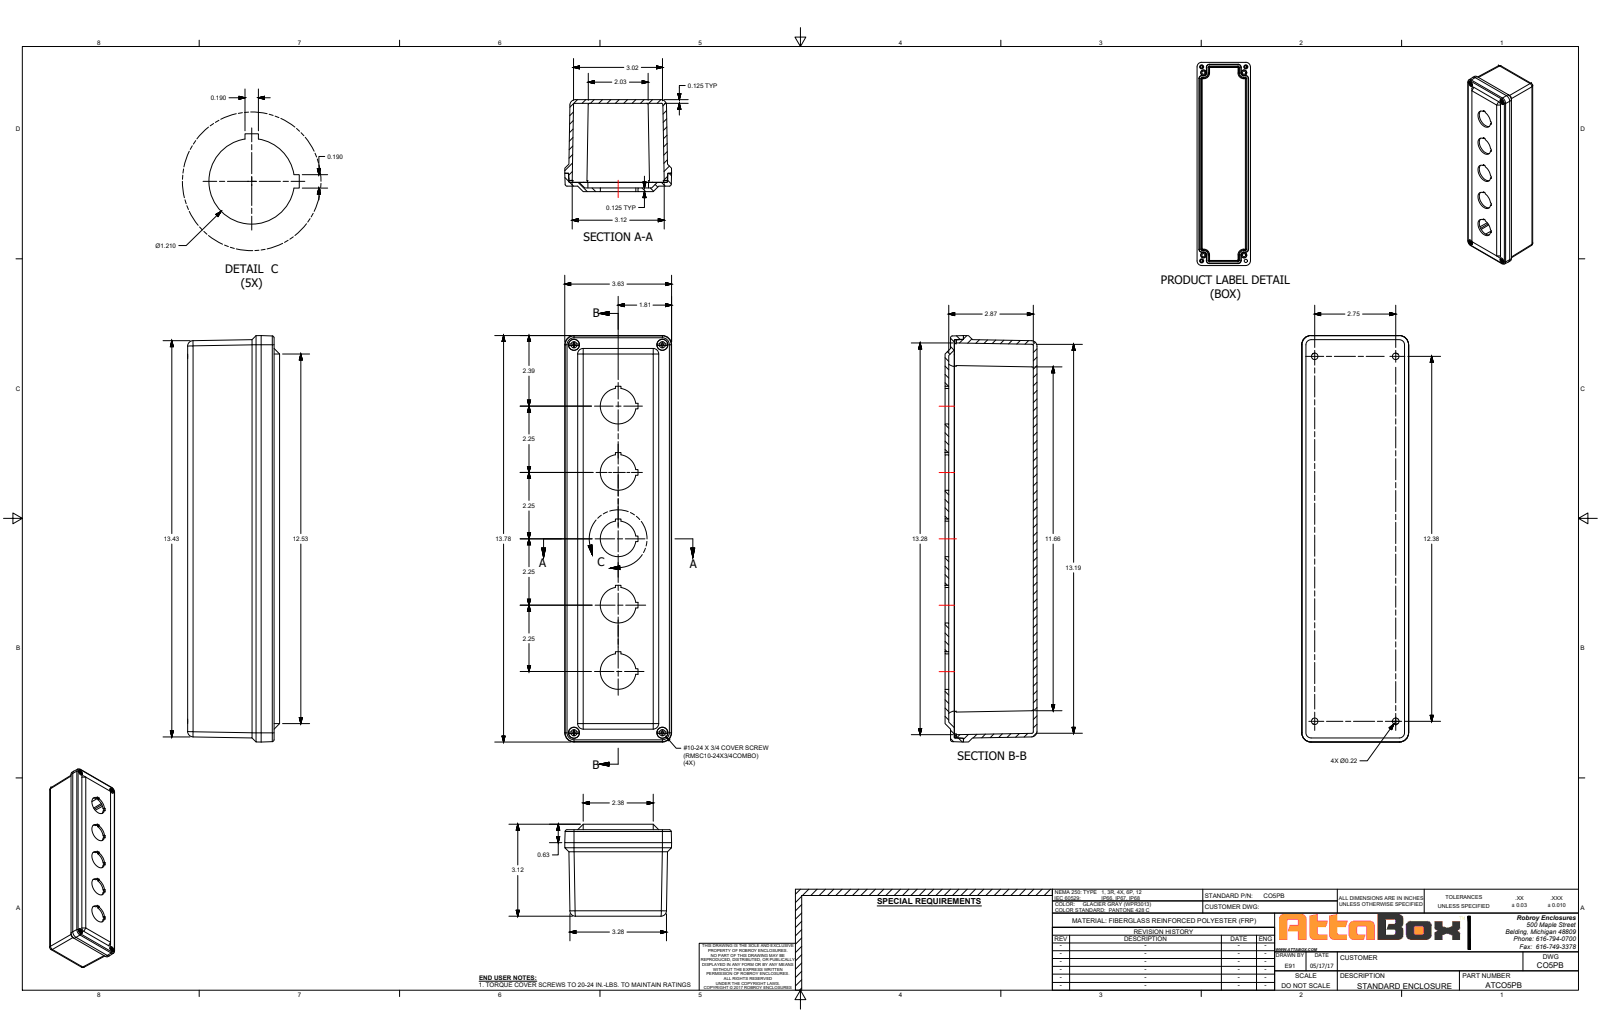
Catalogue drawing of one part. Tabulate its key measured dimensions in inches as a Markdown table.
| quantity | value |
| --- | --- |
| part name | CO5PB |
| STEP written by | SolidWorks 2018 (AUTOMOTIVE_DESIGN) |
| units | inches |
| bodies | 11 solids, 415 faces (197 planar, 122 cylindrical, 96 other) |
| overall size | 13.783 × 3.625 × 3.12 |
| volume | 26.89 in³ |
| surface area | 413.3 in² |
| round holes (diameter × count) | 0.219 × 8, 1.21 × 5, 0.159 × 4, 0.19 × 4, 0.375 × 4 |
| round bosses / shafts (diameter × count) | 0.371 × 4, 0.27 × 4, 0.177 × 4 |
| partial cylindrical surfaces (radius × count) | 0.031 × 20, 0.012 × 16, 0.048 × 8, 0.063 × 4, 0.176 × 4, 0.188 × 4, 0.22 × 4, 0.313 × 4 |
| main face-to-face distances | 0.125, 0.122, 2.995, 3.12, 2.87, 2.807, 0.187, 0.313, 0.125, 0.062 |
| hole center spacings | 0.41, 2.176, 2.25, 2.563, 2.901, 4.17, 4.581, 6.338 |
